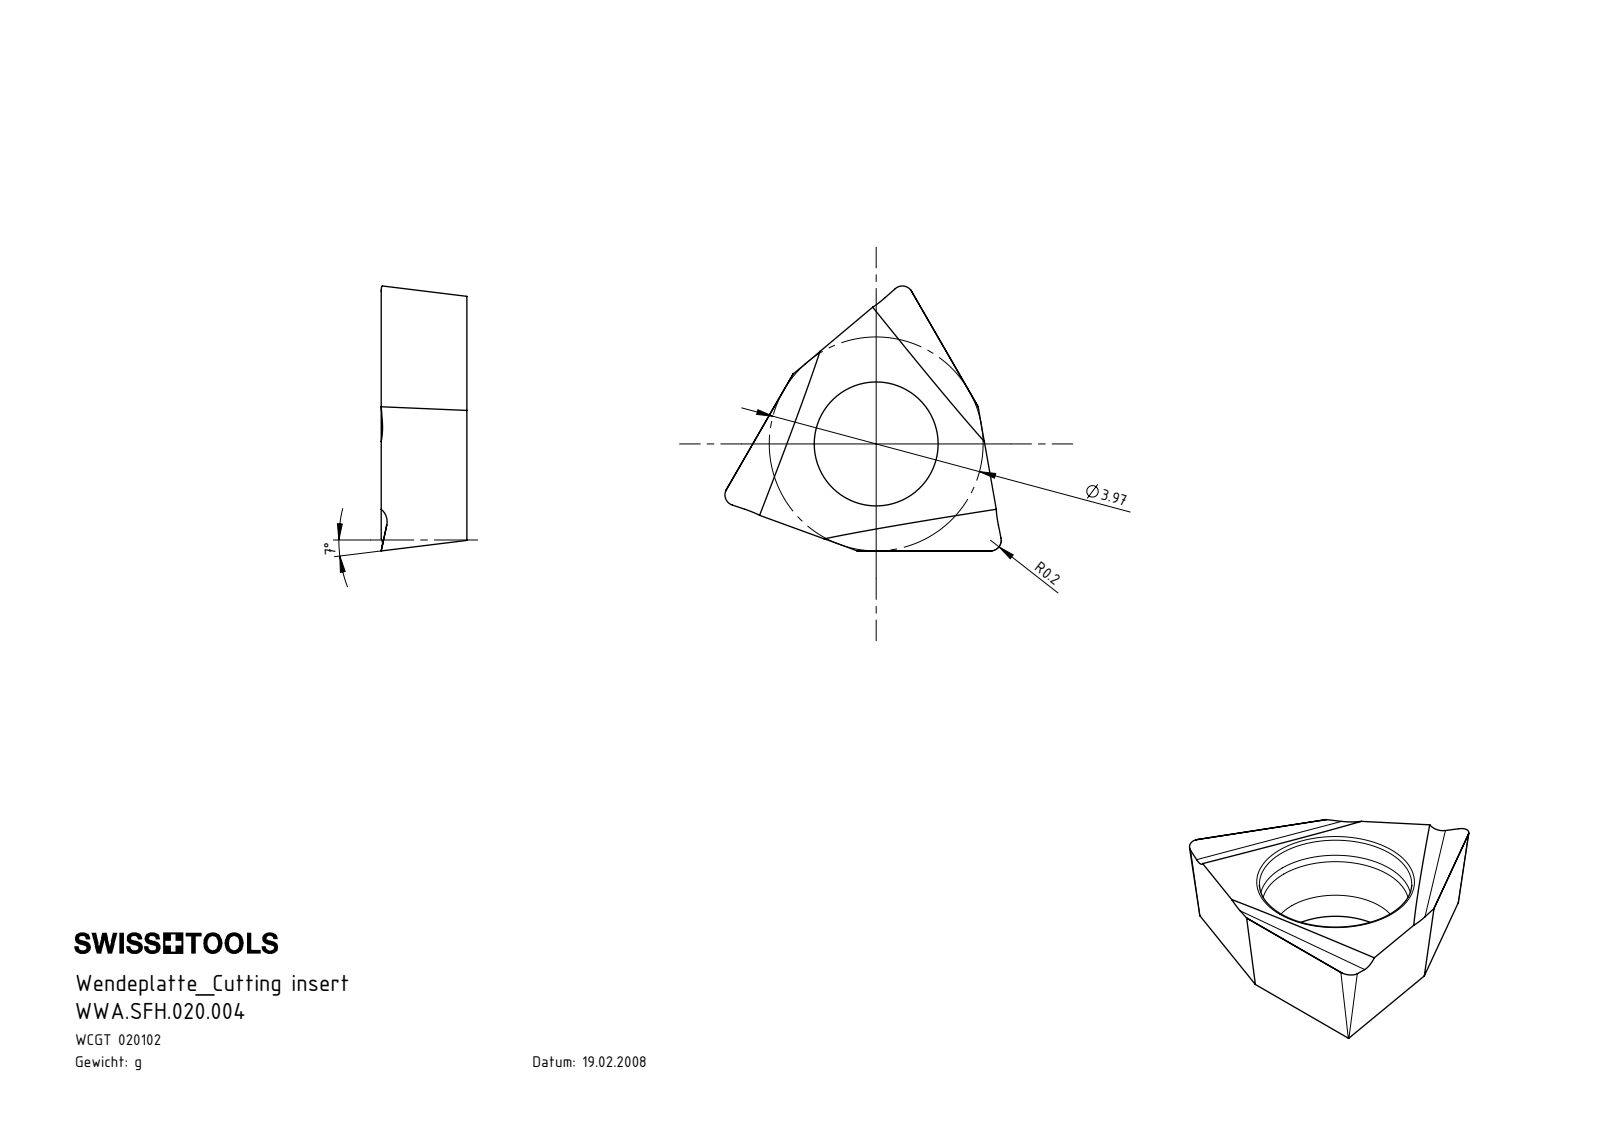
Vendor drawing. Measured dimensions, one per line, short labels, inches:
name: WWA-SFH.020.004
written by: SolidWorks 2017 (AUTOMOTIVE_DESIGN)
unit: in
bodies: 1 solid, 31 faces (14 planar, 5 cylindrical, 12 other)
size: 0.202 × 0.194 × 0.063
volume: 0.001 in³; area: 0.087 in²
holes: 1× ⌀0.091
rounds: 3× R0.012
face distances: 0.063
